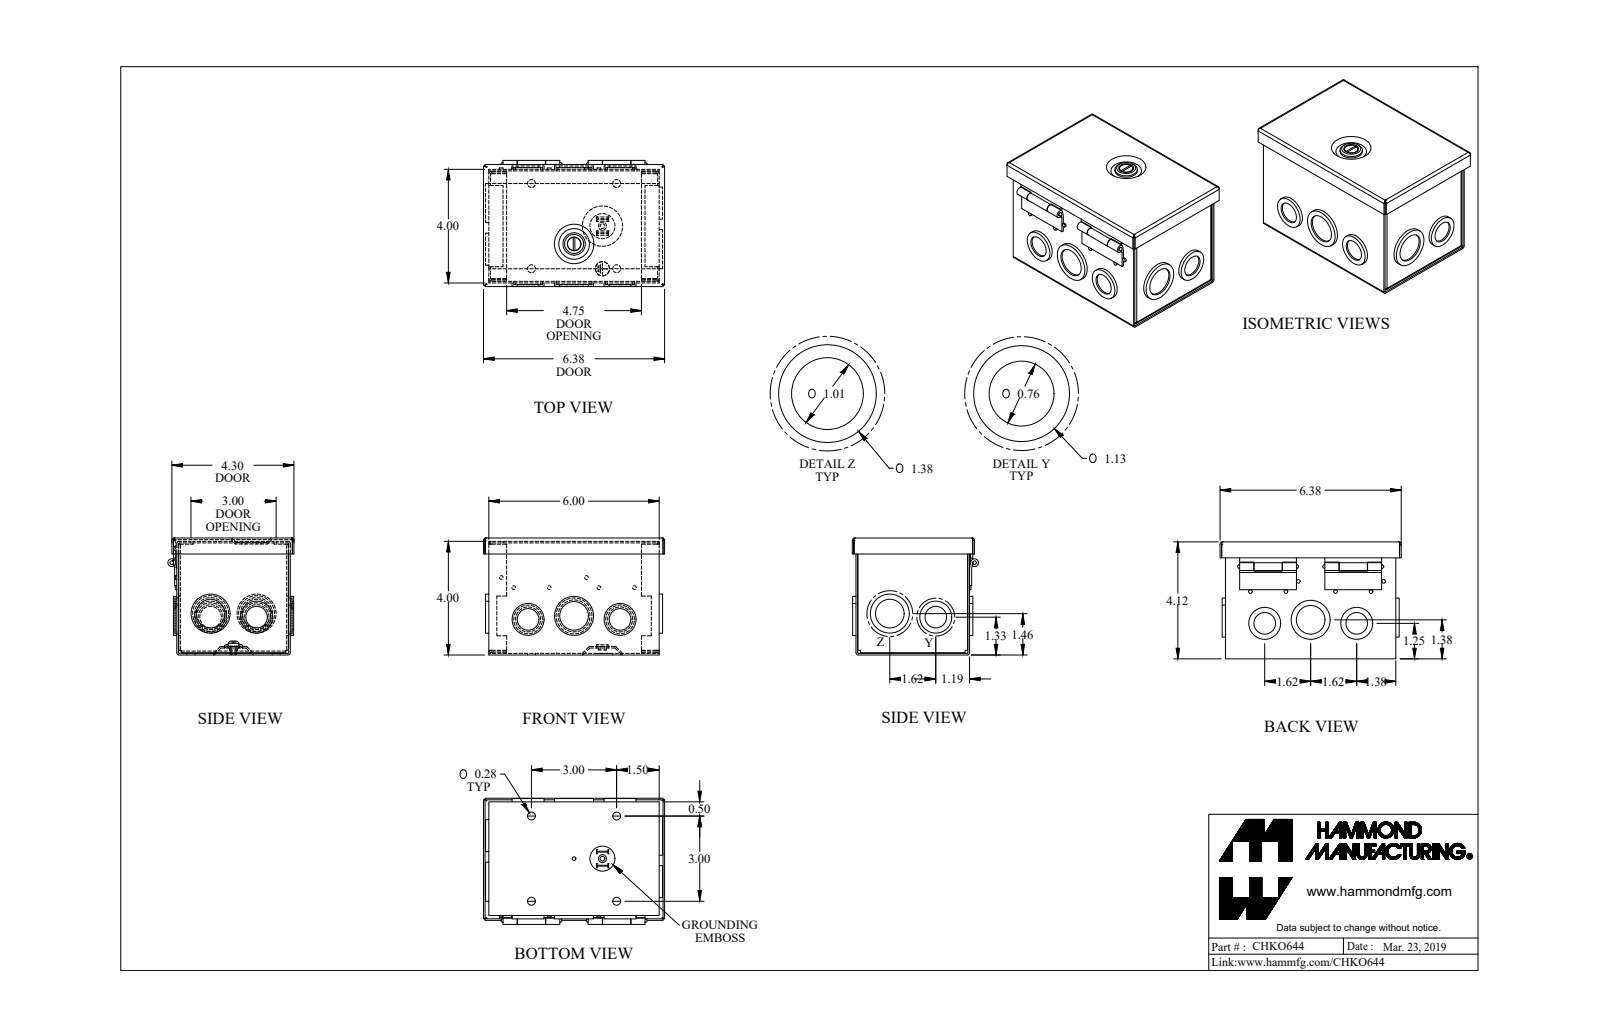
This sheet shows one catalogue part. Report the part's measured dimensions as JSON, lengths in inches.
{"part_name": "CHKO644_Default", "step_written_by": "SolidWorks 2019 (CONFIG_CONTROL_DESIGN)", "units": "inches", "bodies": {"solids": 12, "faces": 623, "planar": 328, "cylindrical": 252, "other": 43}, "overall_size": [6.38, 4.443, 4.118], "volume_in3": 10.22, "surface_area_in2": 358.9, "round_holes": [[1.011, 7], [0.281, 4], [0.761, 4], [1.261, 3], [0.125, 1], [0.17, 1], [0.319, 1], [0.476, 1], [0.5, 1]], "round_bosses_or_shafts": [[0.131, 8], [1.125, 4], [0.875, 4], [1.375, 3], [1.125, 3], [0.875, 2], [0.787, 1], [0.547, 1]], "partial_cylinders_radius": [[0.029, 16], [0.086, 16], [0.057, 8], [0.012, 4], [0.1, 4], [0.036, 2], [0.079, 2], [0.25, 2]], "face_to_face_distances": [0.057, 3.943, 4.061, 4, 3.886, 5.943, 4.118, 4.004, 6, 0.118], "hole_center_spacings": [3, 0.125, 1.581, 1.62, 1.624, 1.625, 2.915, 4.243]}
